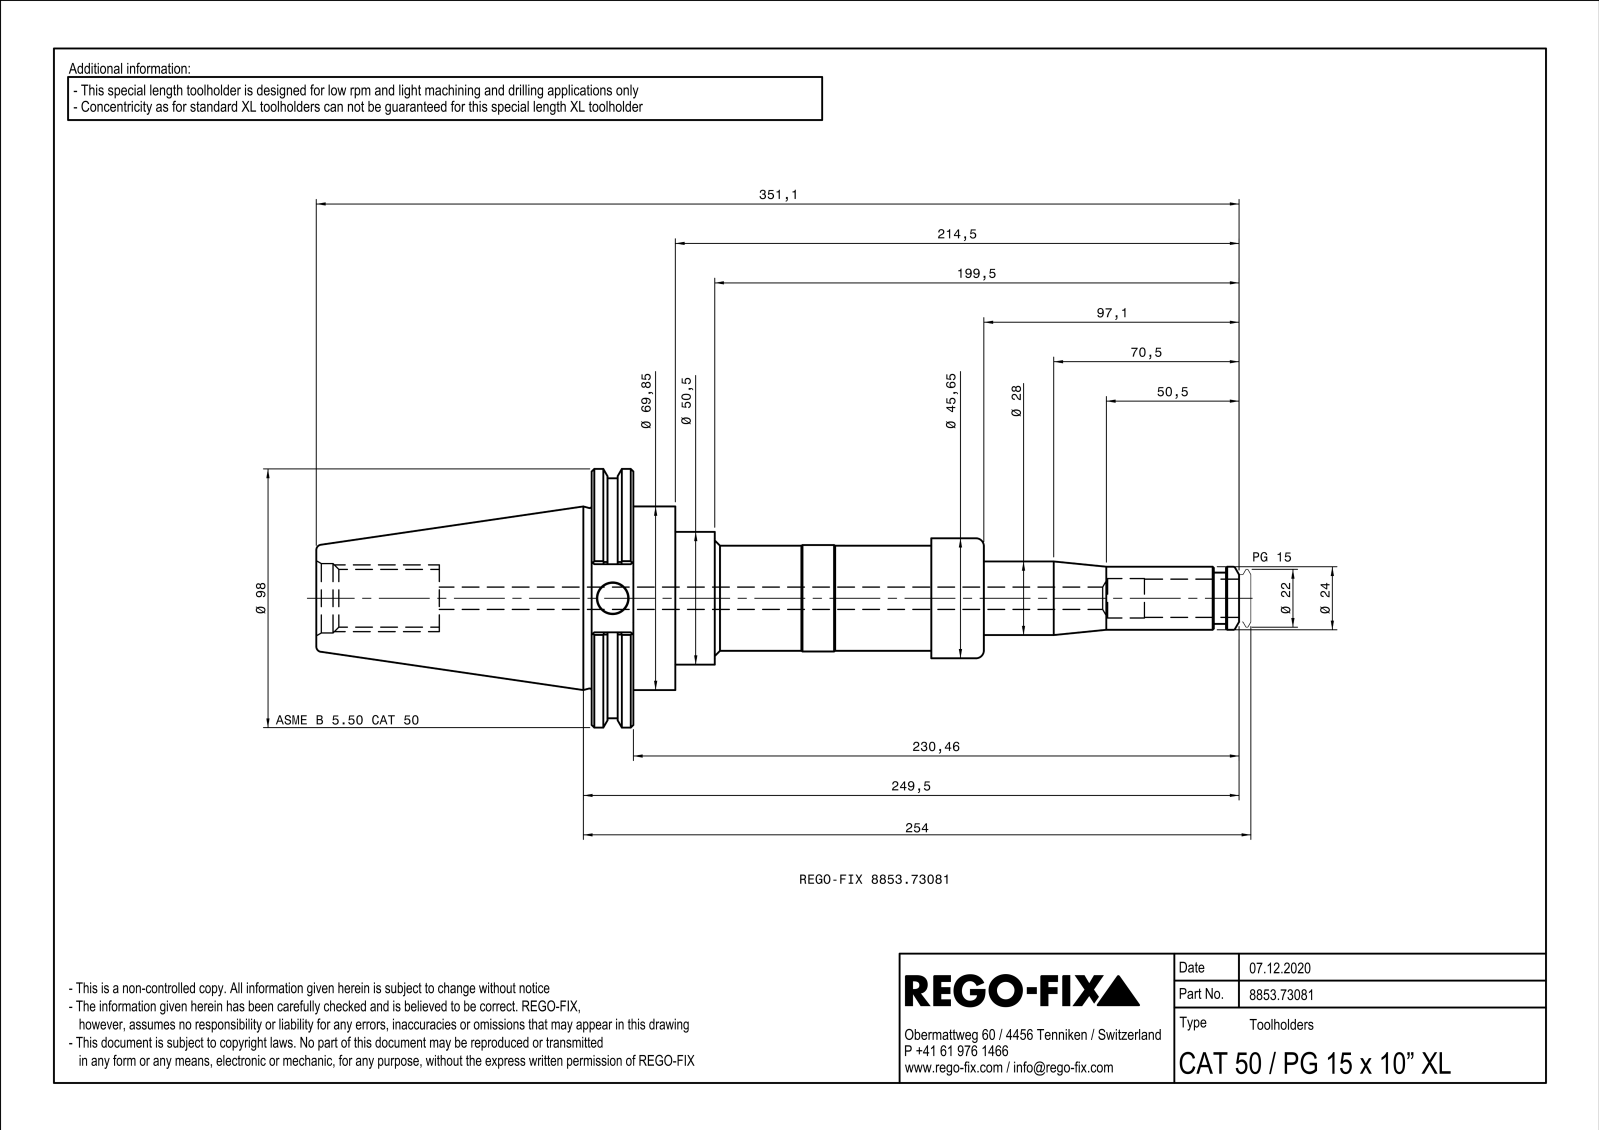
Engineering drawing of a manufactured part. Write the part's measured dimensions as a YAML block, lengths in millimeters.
part_name: "NOCUT"
step_written_by: "SIEMENS PLM Software Solid Edge ST10 (AUTOMOTIVE_DESIGN)"
units: millimeters
bodies: {solids: 1, faces: 171, planar: 48, cylindrical: 46, other: 77}
overall_size: [351.1, 98.42, 94.39]
volume: 540787
surface_area: 89234
round_holes:
  - {diameter: 9, count: 1}
  - {diameter: 10, count: 1}
  - {diameter: 11.7, count: 1}
  - {diameter: 13, count: 1}
  - {diameter: 15, count: 1}
  - {diameter: 21.96, count: 1}
  - {diameter: 25, count: 1}
  - {diameter: 26.4, count: 1}
  - {diameter: 29, count: 1}
  - {diameter: 38.38, count: 1}
  - {diameter: 40.05, count: 1}
  - {diameter: 43.3, count: 1}
round_bosses_or_shafts:
  - {diameter: 98.42, count: 1}
  - {diameter: 91.3, count: 1}
  - {diameter: 69.85, count: 1}
  - {diameter: 50.5, count: 1}
  - {diameter: 45.65, count: 1}
  - {diameter: 40.5, count: 1}
  - {diameter: 40, count: 1}
  - {diameter: 34, count: 1}
partial_cylinders:
  - {radius: 0.5, count: 12}
  - {radius: 22.77, count: 1}
face_to_face_distances: [15.87, 15.96, 31.83, 117.4, 133.36, 149.23, 6, 14, 254, 136.6]
